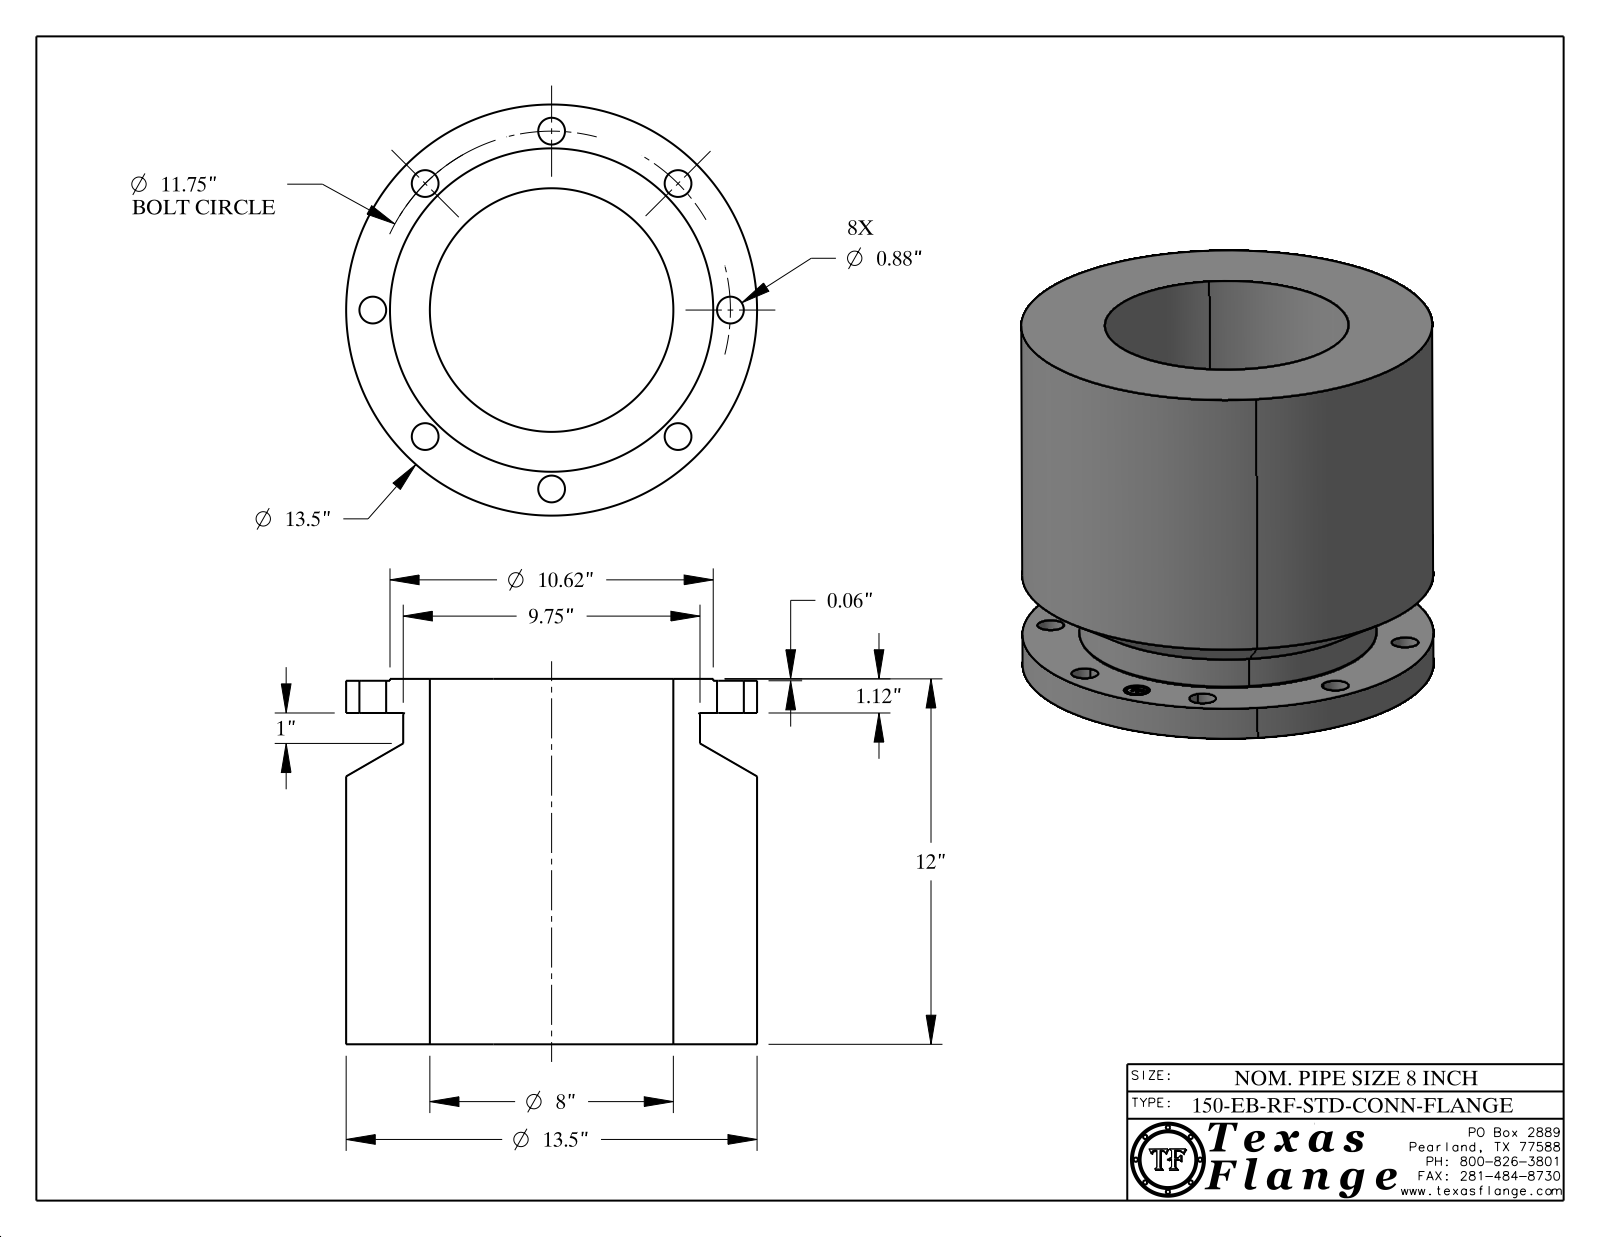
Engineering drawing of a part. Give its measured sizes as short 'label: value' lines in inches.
name: 8-150-EB-RF-STD-CONN-FLANGE
written by: CATIA V5 STEP AP214 (AUTOMOTIVE_DESIGN)
unit: in
bodies: 1 solid, 421 faces (369 planar, 46 cylindrical, 6 other)
size: 13.5 × 13.5 × 12
volume: 998.4 in³; area: 1 100 in²
holes: 8× ⌀0.88, 1× ⌀0.85, 1× ⌀8
bosses: 8× ⌀0.051, 1× ⌀13.5, 1× ⌀10.62, 1× ⌀9.75, 1× ⌀0.67
face distances: 10.88, 1.057, 11.937, 0.063, 1.12, 12, 1.115, 1.052, 10.885, 0.254
hole spacings: 5.875, 4.496, 8.309, 10.856, 11.75, 9.77, 2.292, 2.293
